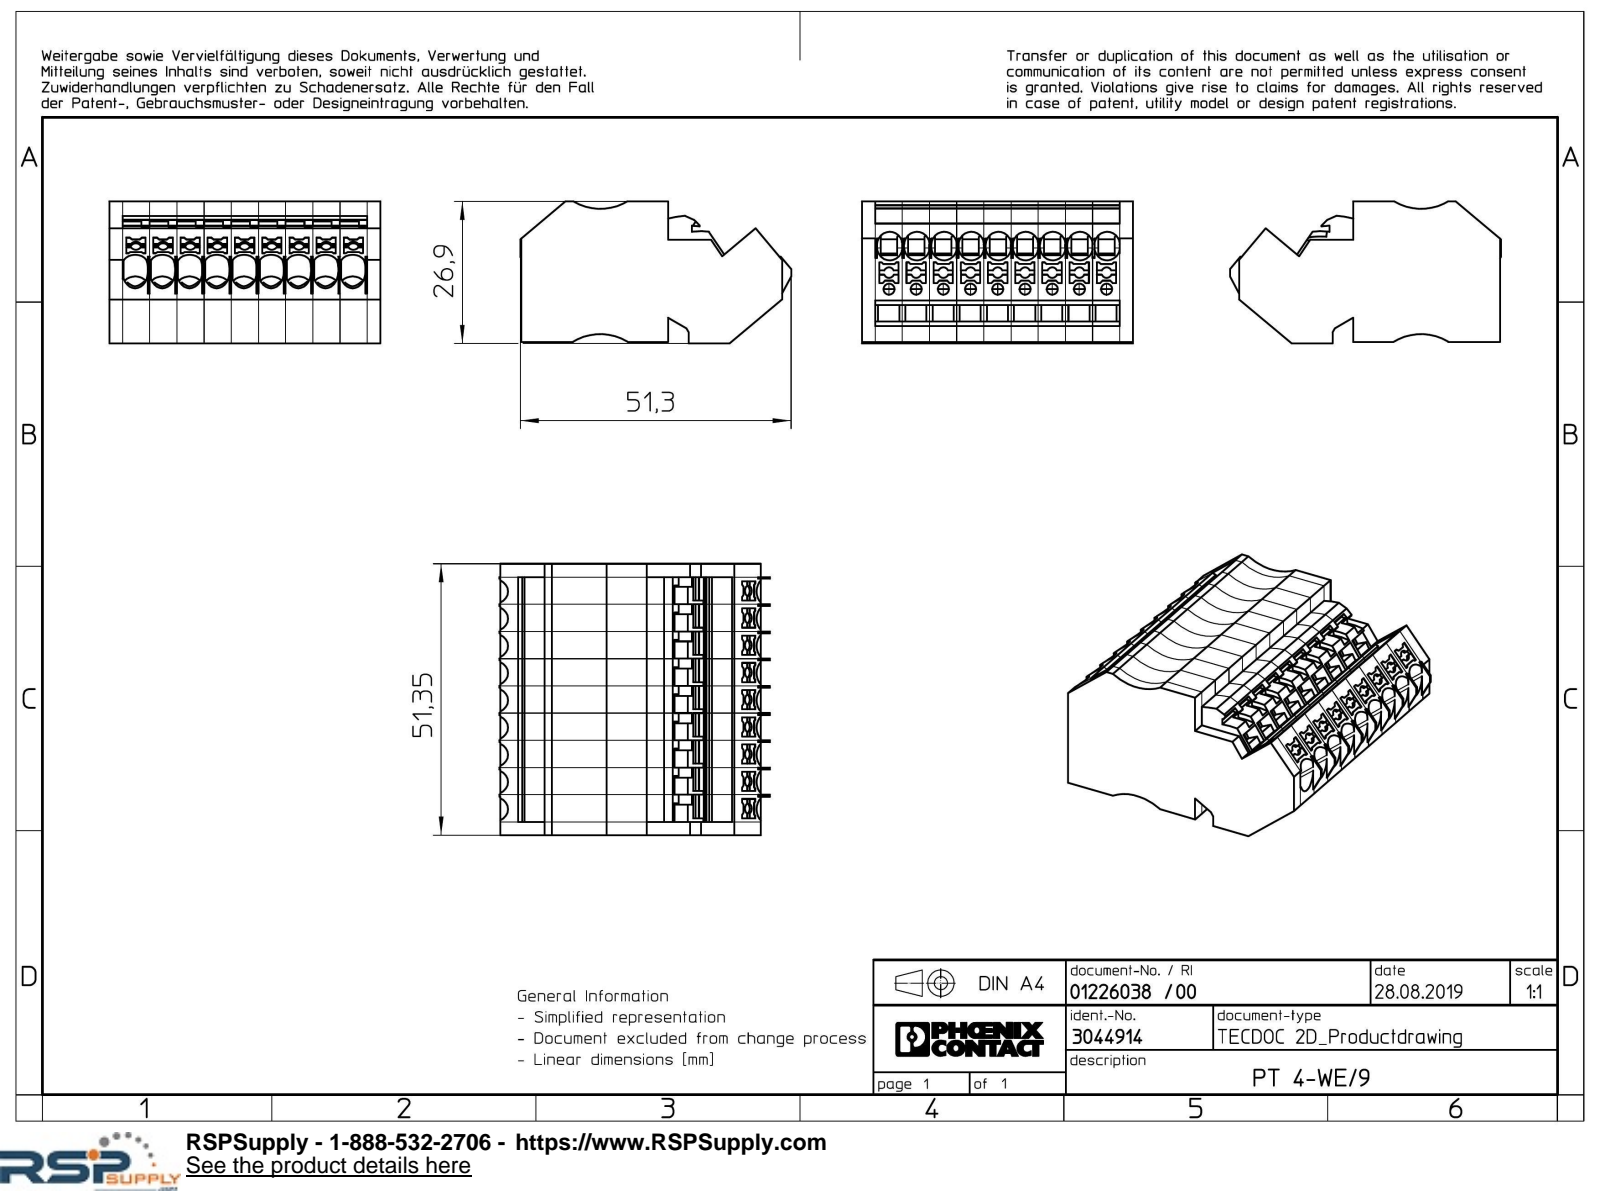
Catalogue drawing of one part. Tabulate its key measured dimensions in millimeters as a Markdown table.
| quantity | value |
| --- | --- |
| part name | PT_4_WE_9-select |
| STEP written by | Creo Elements/Direct Modeling 20.1A 29-Sep-2018 (C) Parametric Technology GmbH (AUTOMOTIVE_DESIGN) |
| units | millimeters |
| bodies | 1 solid, 1527 faces (1325 planar, 184 cylindrical, 18 other) |
| overall size | 51.35 × 51.3 × 26.9 |
| volume | 46 535 mm³ |
| surface area | 18 357 mm² |
| round holes (diameter × count) | 2.1 × 9 |
| partial cylindrical surfaces (radius × count) | 2.4 × 36, 1 × 18, 1.03 × 3, 10 × 2, 1.05 × 1, 1.78 × 1, 12.4 × 1, 13.38 × 1 |
| main face-to-face distances | 51.35, 5.15, 10.3, 3.15, 3.85, 7, 7.2, 27.8, 15.45, 19.6 |
| hole center spacings | 5.15, 10.3, 15.45, 20.6, 25.75, 30.9, 36.05, 41.2 |
